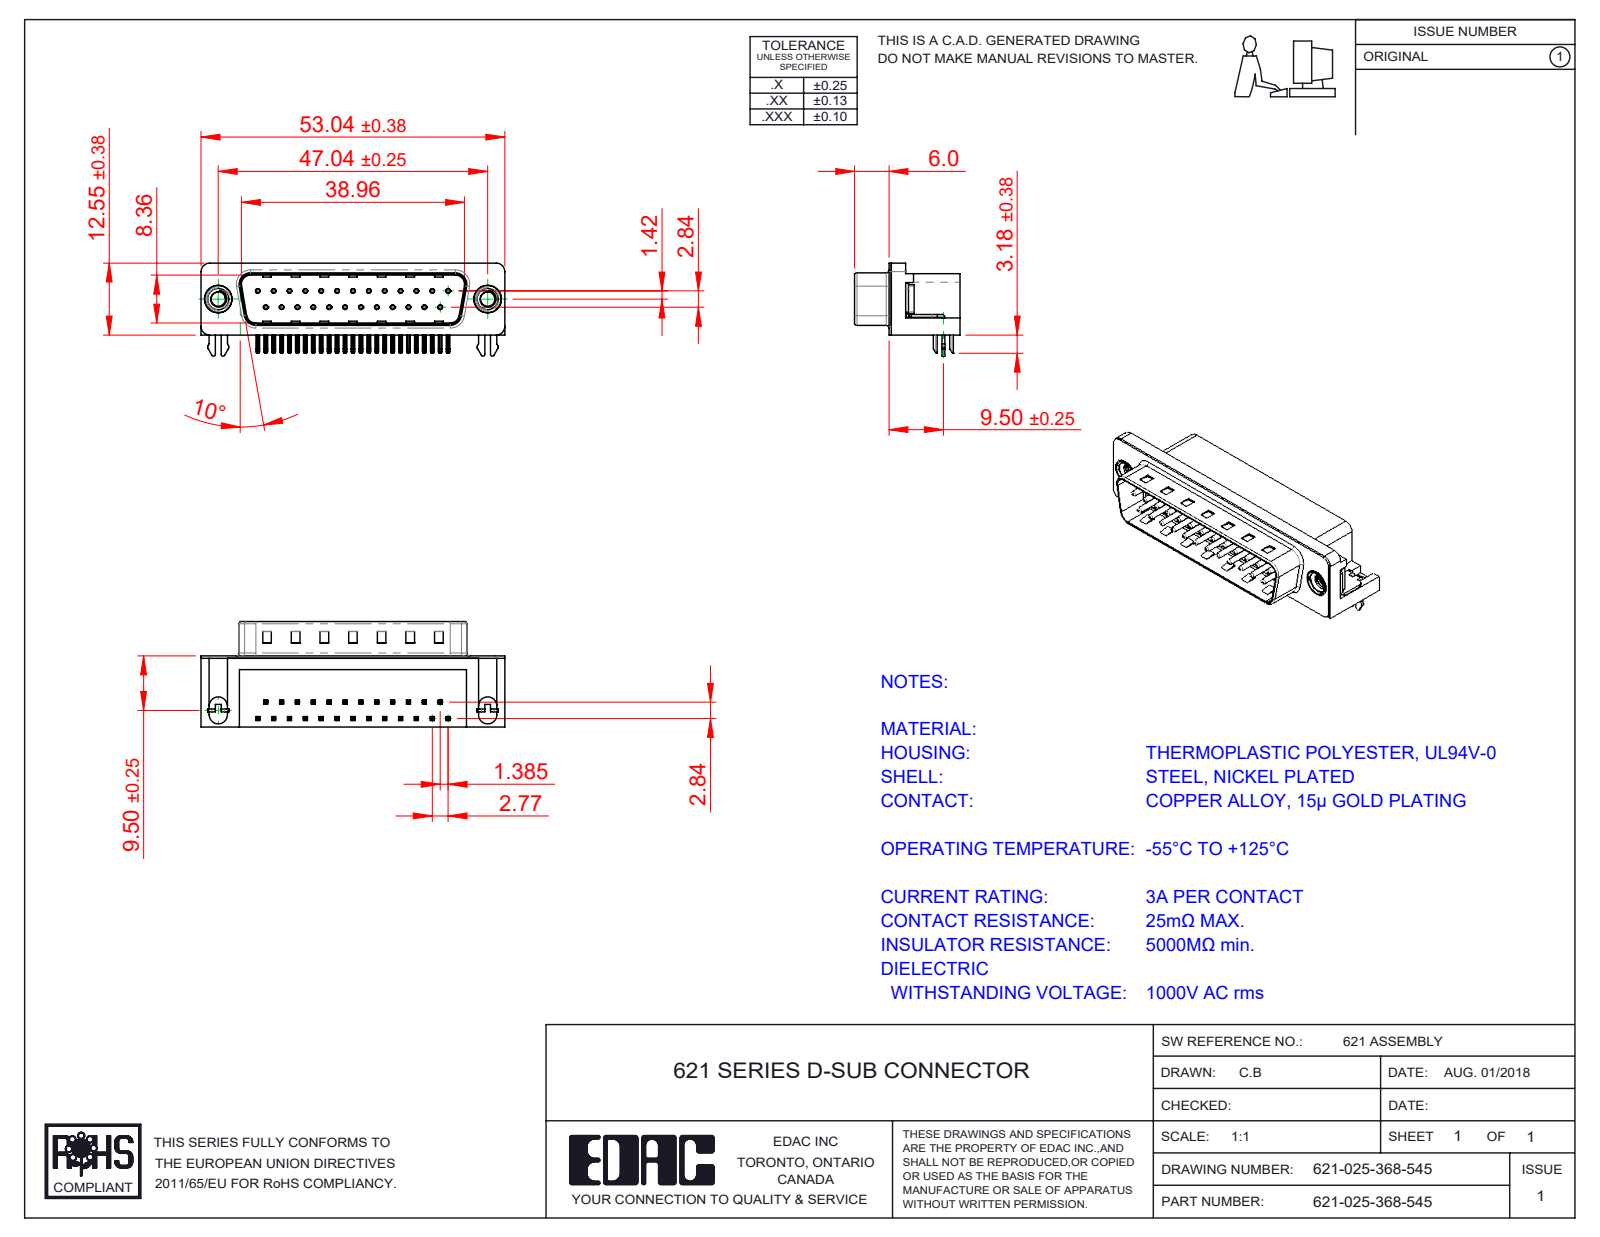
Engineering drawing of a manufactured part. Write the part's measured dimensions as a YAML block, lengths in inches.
part_name: "621 M3 Threaded Rivet; 621 Contact Bottom; 621 Housing_25 Socket; 621 Contact Top (+3 more)"
step_written_by: "SolidWorks 2016 (CONFIG_CONTROL_DESIGN)"
units: inches
bodies: {solids: 31, faces: 2383, planar: 1447, cylindrical: 669, other: 267}
overall_size: [2.088, 0.724, 0.64]
volume: 0.388
surface_area: 12.03
round_holes:
  - {diameter: 0.014, count: 25}
  - {diameter: 0.031, count: 25}
  - {diameter: 0.079, count: 2}
  - {diameter: 0.098, count: 2}
  - {diameter: 0.157, count: 2}
  - {diameter: 0.189, count: 2}
  - {diameter: 0.197, count: 2}
round_bosses_or_shafts:
  - {diameter: 0.03, count: 25}
  - {diameter: 0.193, count: 2}
  - {diameter: 0.187, count: 2}
  - {diameter: 0.154, count: 2}
  - {diameter: 0.118, count: 2}
partial_cylinders:
  - {radius: 0.01, count: 112}
  - {radius: 0.005, count: 50}
  - {radius: 0.039, count: 16}
  - {radius: 0.02, count: 9}
  - {radius: 0.063, count: 8}
  - {radius: 0.059, count: 7}
  - {radius: 0.035, count: 4}
  - {radius: 0.079, count: 4}
face_to_face_distances: [0.016, 0.472, 0.407, 0.083, 0.345, 0.412, 0.067, 0.428, 0.488, 0.354]
hole_center_spacings: [0.124, 0.109, 0.218, 0.327, 0.436, 0.545, 0.654, 0.198]
